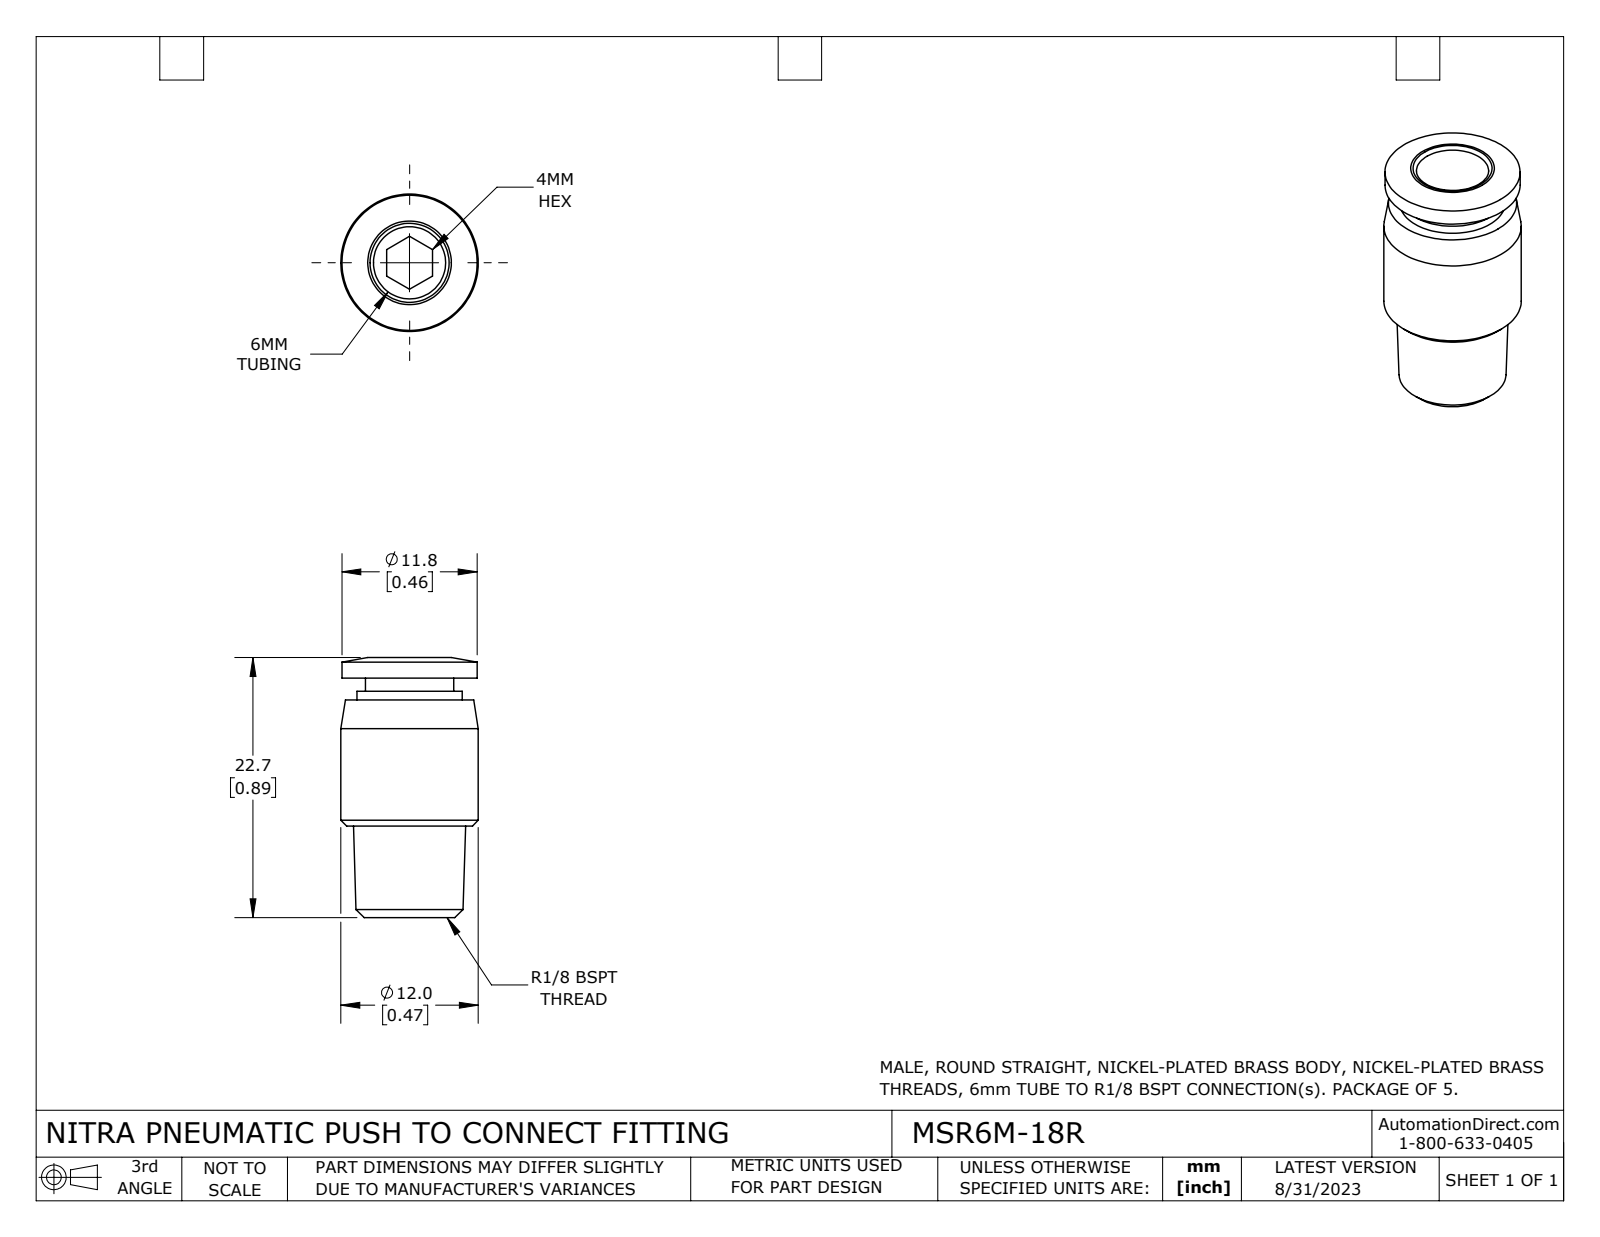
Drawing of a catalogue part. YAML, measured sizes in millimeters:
part_name: "MSR6M-18R"
step_written_by: "SolidWorks 2015 (AUTOMOTIVE_DESIGN)"
units: millimeters
bodies: {solids: 1, faces: 31, planar: 7, cylindrical: 12, other: 12}
overall_size: [22.7, 12, 12]
volume: 1500
surface_area: 1437
round_holes:
  - {diameter: 4, count: 1}
  - {diameter: 6.3, count: 1}
round_bosses_or_shafts:
  - {diameter: 12, count: 1}
  - {diameter: 11.8, count: 1}
  - {diameter: 9.2, count: 1}
  - {diameter: 7.7, count: 1}
face_to_face_distances: [20.9, 19, 1.9, 19.8, 0.8, 1.1, 8, 11, 11.8, 12.9]
